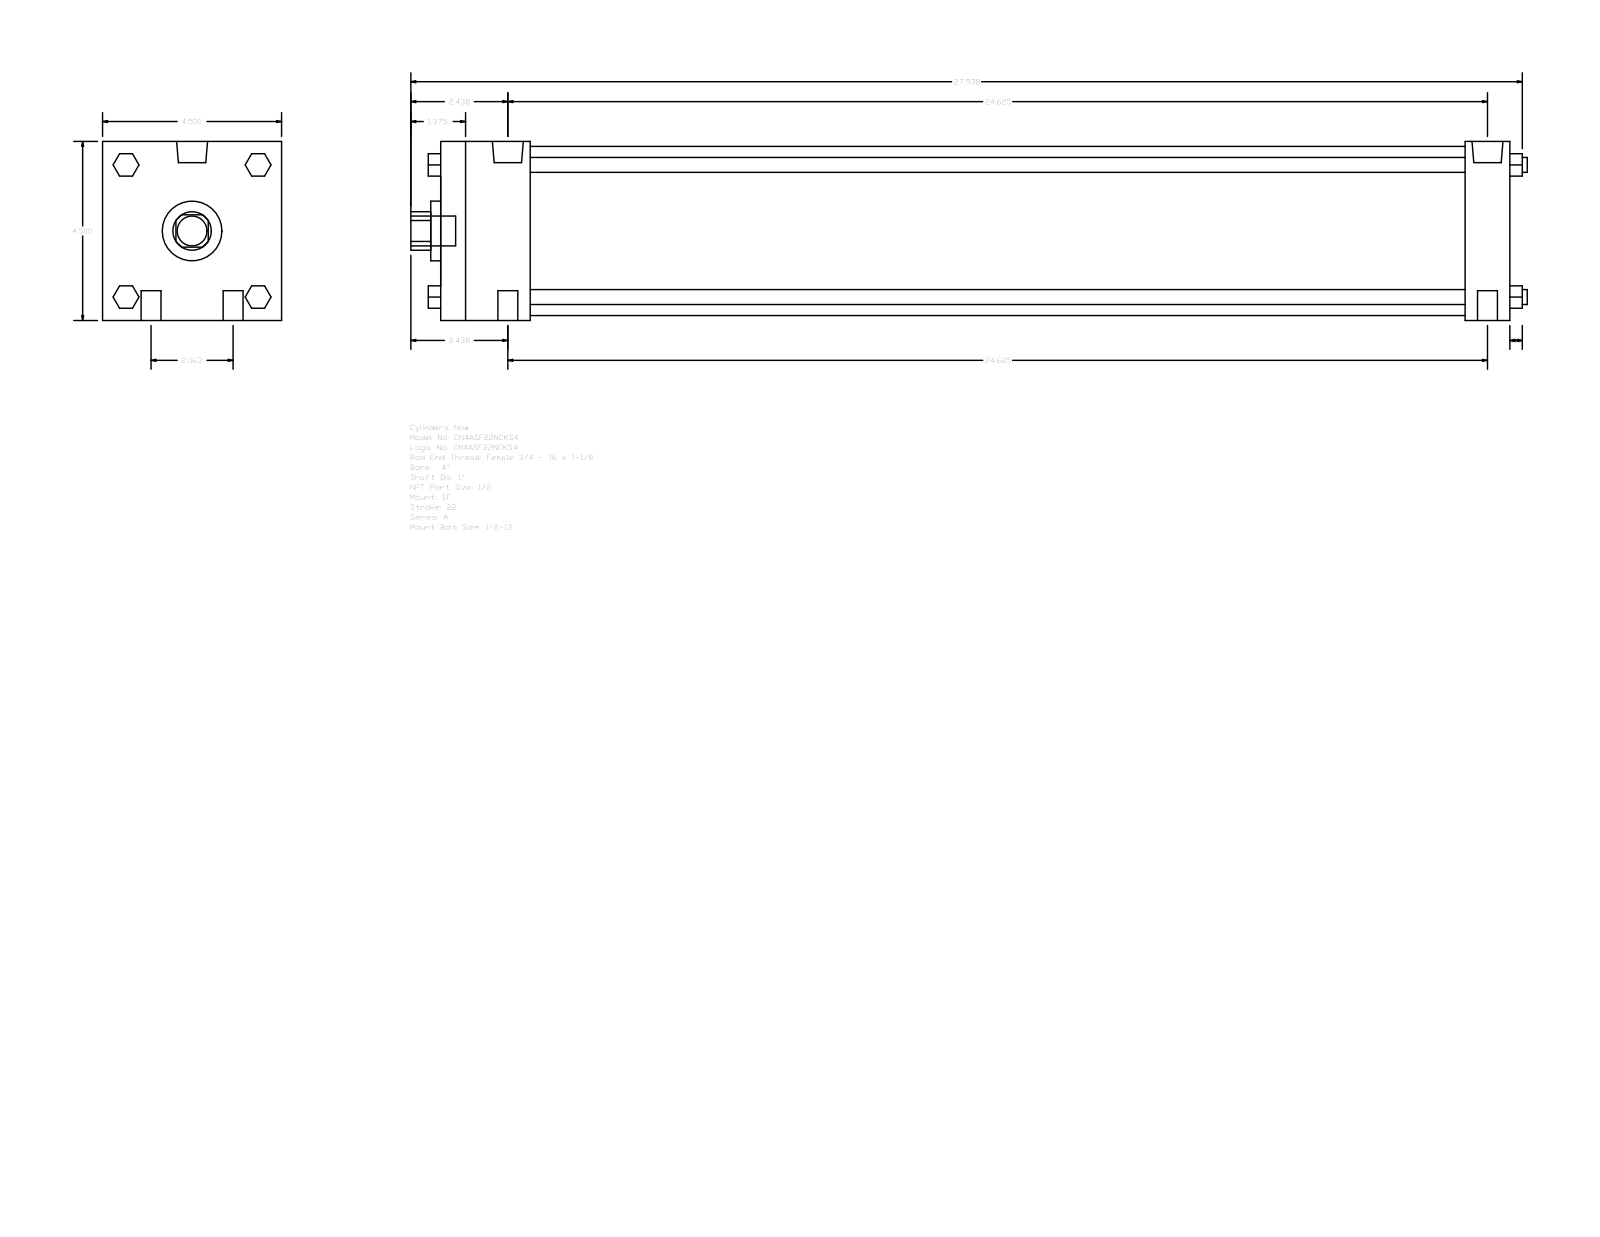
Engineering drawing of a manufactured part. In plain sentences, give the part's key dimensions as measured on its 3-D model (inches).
The part is named "A_SF__0400_1". Its 3-D file was written by "GSSL Pune (CONFIG_CONTROL_DESIGN)". It is 0 solids with 124 faces: 94 planar, 30 cylindrical and 0 other. Overall it measures 28.063 by 4.5 by 4.5 inches. Round holes: 1 of diameter 1, 1 of diameter 1.5, 1 of diameter 4.25. Round bosses or shafts: 4 of diameter 0.5, 4 of diameter 0.375, 2 of diameter 0.778, 2 of diameter 0.344, 1 of diameter 0.75. Partial cylindrical surfaces (rounded edges, fillets, slot ends): 1 of radius 0.484. The main face-to-face distances are 4.5, 26.875, 1.125, 25.75, 2.25, 23.5, 24.625, 0.563, 1.66, 2.875.
